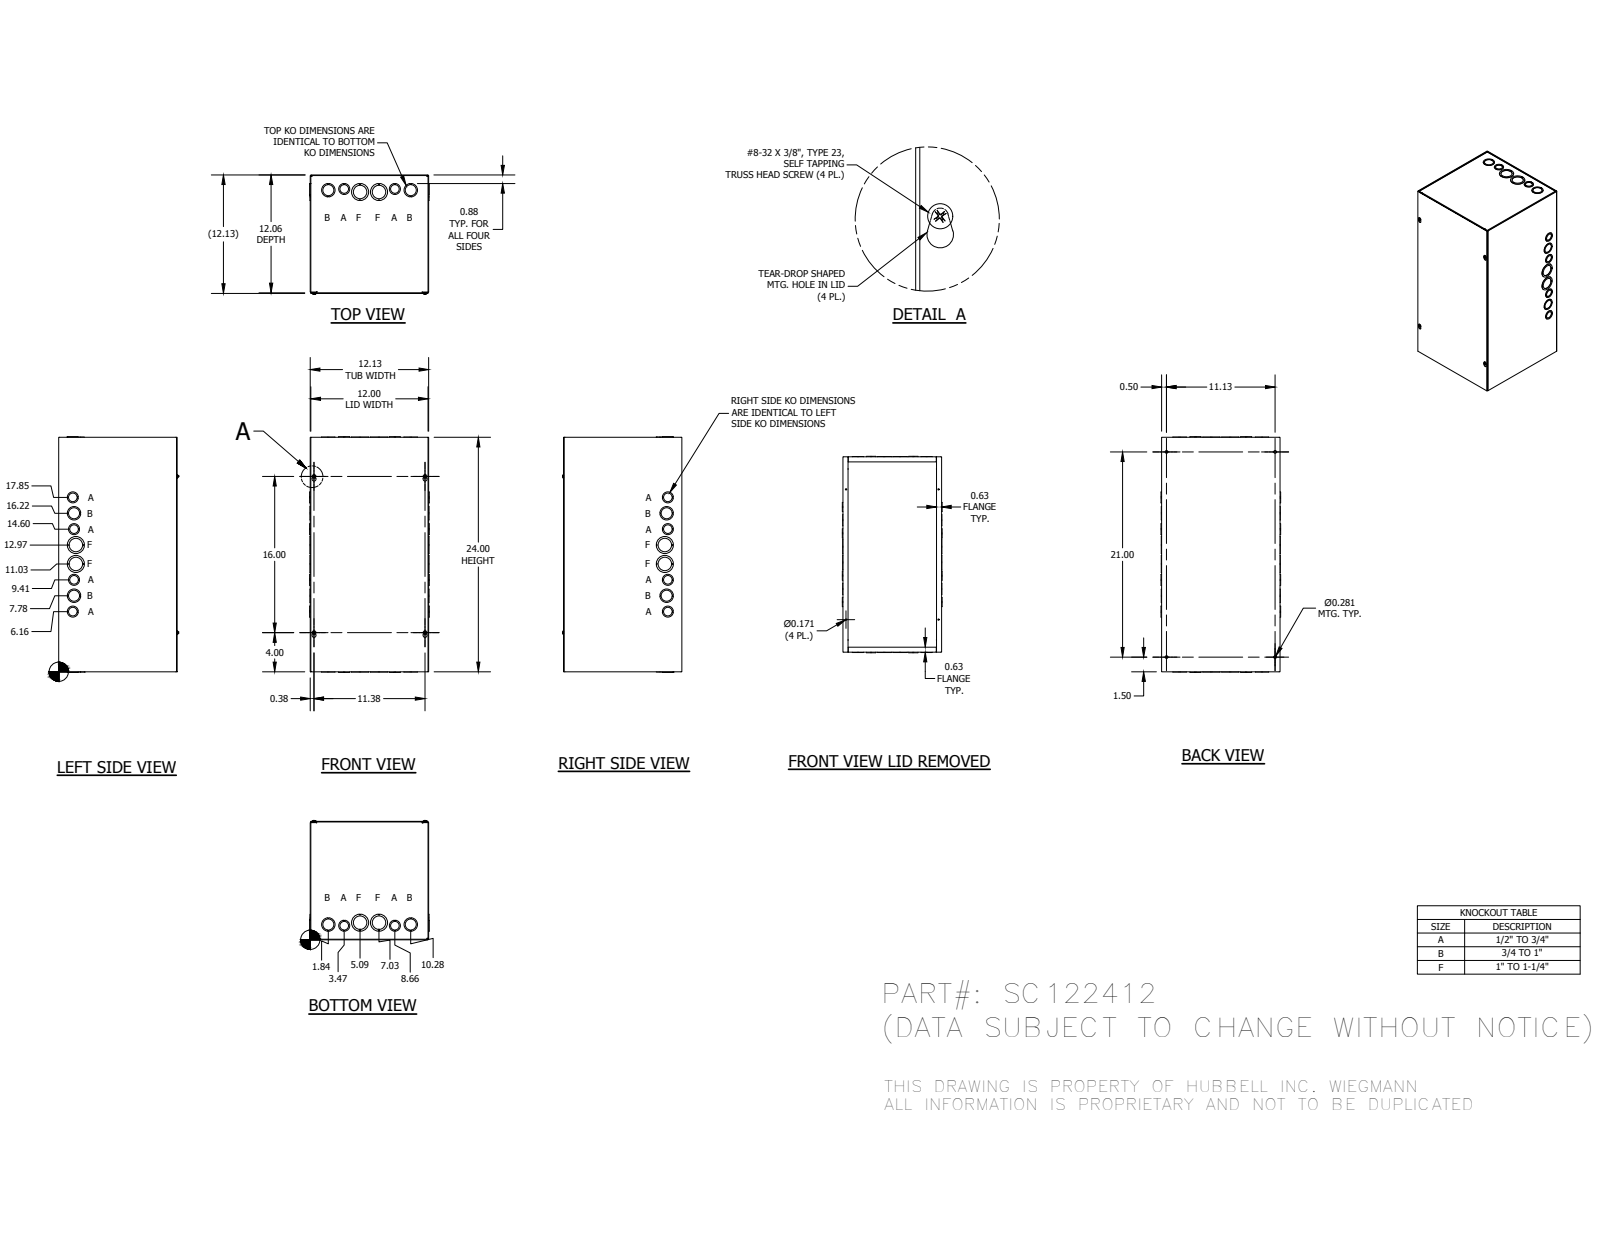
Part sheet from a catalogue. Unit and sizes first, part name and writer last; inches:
Units: inches
Overall size (bounding box): 24.125 × 12.25 × 12.225
Round holes (diameter × count): ⌀1.125 ×12, ⌀0.875 ×8, ⌀1.375 ×8, ⌀0.171 ×4, ⌀0.281 ×4, ⌀1.75 ×4
Round bosses / shafts (diameter × count): ⌀0.384 ×4, ⌀0.164 ×4
Partial cylindrical surfaces — rounded edges, fillets, slot ends (radius × count): R0.031 ×12, R0.094 ×12, R0.125 ×4, R0.203 ×4
Main face-to-face distances: 0.063, 12.063, 12, 12.125, 23.937, 24, 23.875, 0.125, 11.937, 0.031
Hole centre spacings: 1.63, 1.655, 2.503, 3.256, 3.579, 5.194, 6.816, 11.524
Bodies: 29 solids, 1055 faces (771 planar, 216 cylindrical, 68 other)
Part name (STEP PRODUCT): SC122412BLR; SC1212TB; SC1224LPA; 34056 (+1 more)
STEP written by: Autodesk Inventor 2014 (AUTOMOTIVE_DESIGN)
